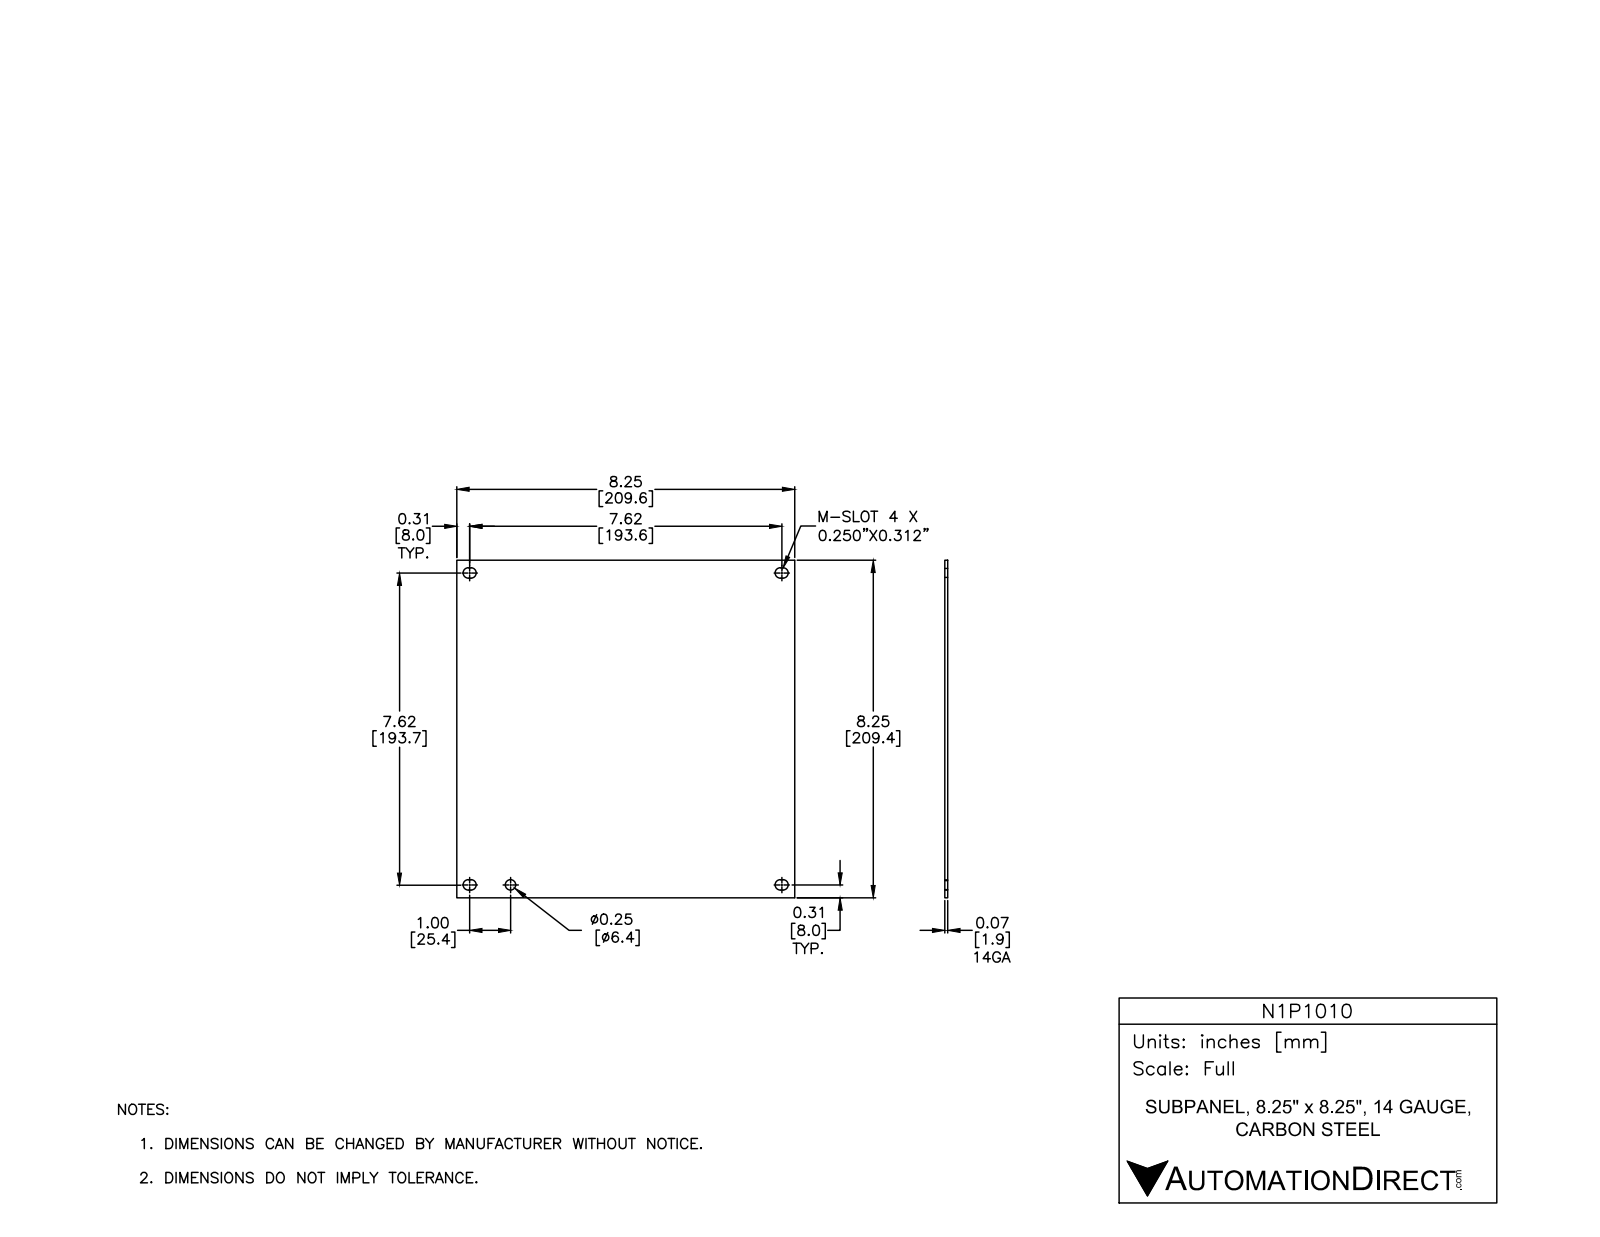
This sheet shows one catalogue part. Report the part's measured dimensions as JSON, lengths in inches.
{"part_name": "N1P1010", "step_written_by": "Autodesk Inventor 2012 (AUTOMOTIVE_DESIGN)", "units": "inches", "bodies": {"solids": 1, "faces": 23, "planar": 14, "cylindrical": 9, "other": 0}, "overall_size": [8.25, 8.25, 0.074], "volume_in3": 5.014, "surface_area_in2": 138.3, "round_holes": [[0.25, 1]], "partial_cylinders_radius": [[0.125, 8]], "face_to_face_distances": [0.074, 8.25, 0.188, 0.438, 7.812, 8.062, 0.25, 7.624, 7.874, 7.374]}
